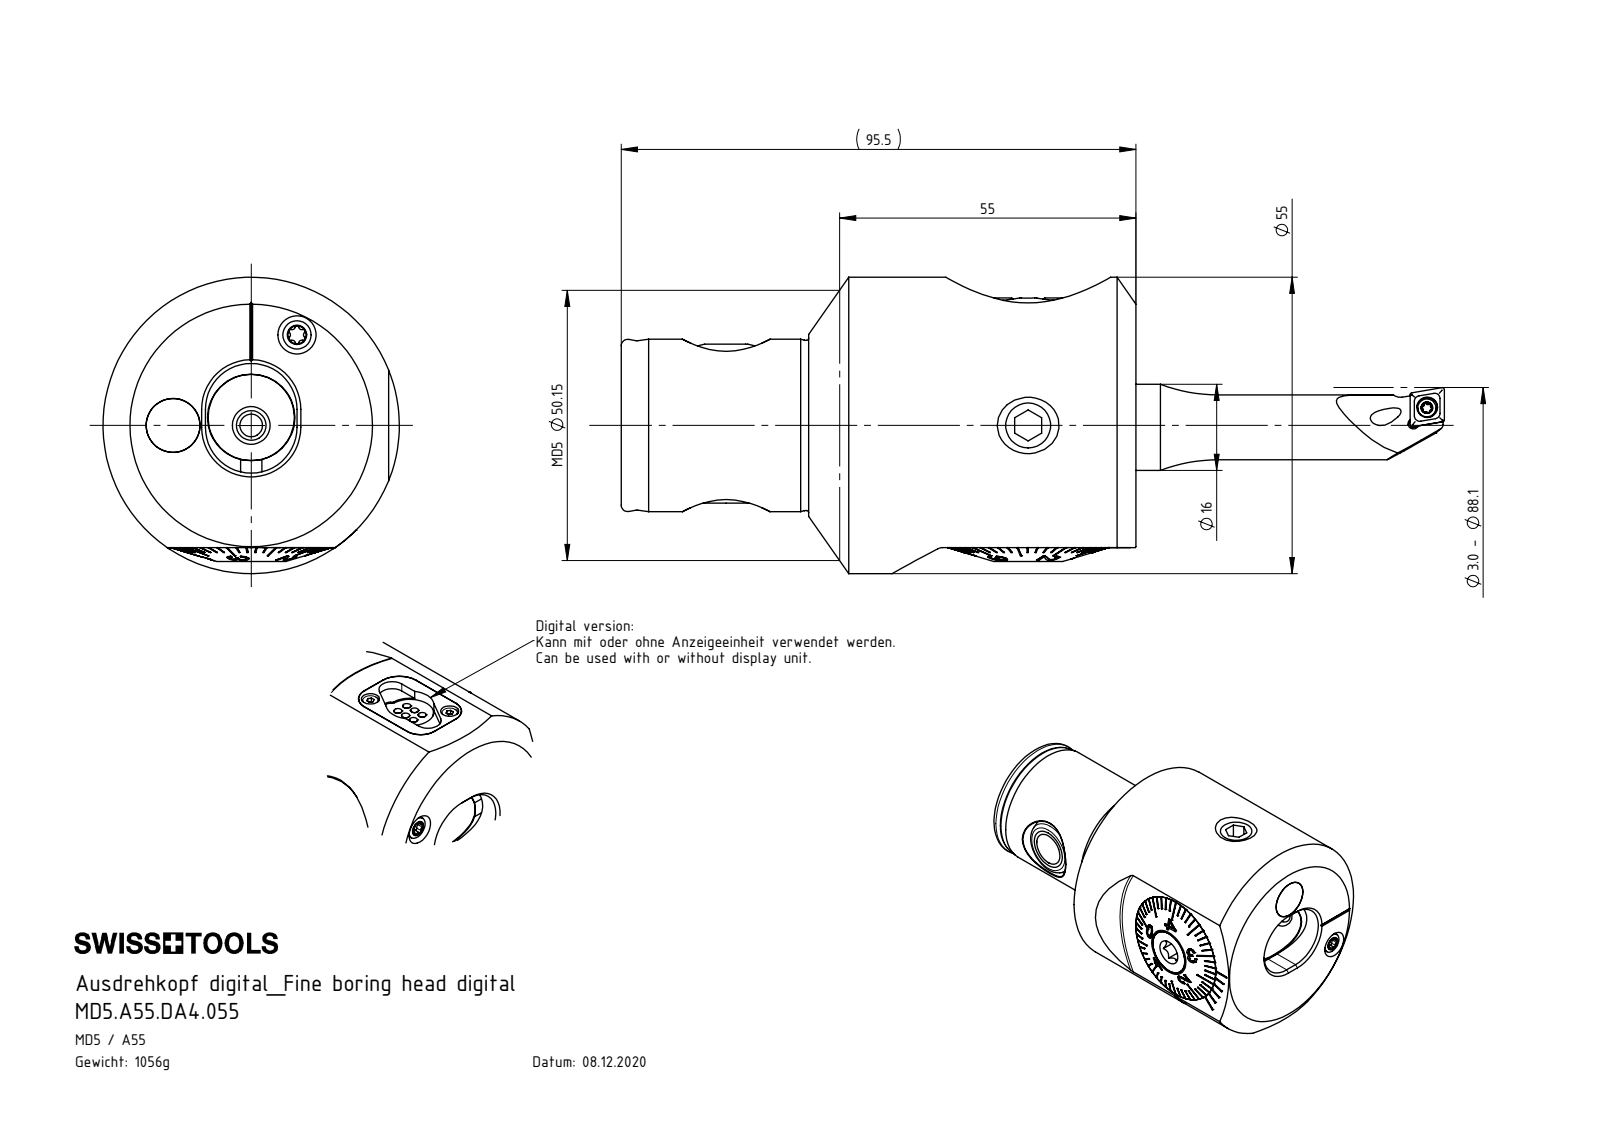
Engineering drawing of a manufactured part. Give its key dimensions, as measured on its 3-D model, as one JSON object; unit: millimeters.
{"part_name": "A55-BG1.DA4.041; DIN 3771 - 17x2; ISO 4026 - M10 x 16_PreviewCfg; Klebstoff D10 (+8 more)", "step_written_by": "SolidWorks 2017 (AUTOMOTIVE_DESIGN)", "units": "millimeters", "bodies": {"solids": 38, "faces": 1147, "planar": 505, "cylindrical": 246, "other": 396}, "overall_size": [95.54, 55, 55], "volume_mm3": 137303, "surface_area_mm2": 48089, "round_holes": [[4.2, 4], [1.6, 3], [8.5, 3], [2.2, 2], [10, 2], [3.3, 1], [6, 1], [7, 1], [8, 1], [8.75, 1], [10.1, 1], [11, 1]], "round_bosses_or_shafts": [[1.9, 6], [10, 4], [3.8, 2], [2, 2], [55, 1], [32, 1], [31.6, 1], [30, 1]], "partial_cylinders_radius": [[0.34, 6], [0.59, 6], [1.1, 6], [1.2, 6], [0.5, 4], [0.8, 4], [1.4, 4], [1.9, 4]], "face_to_face_distances": [95.54, 5.3, 7.13, 4.63, 2.5, 1.83, 2.8, 8.33, 6.5, 3.7], "hole_center_spacings": [7.25, 9.52, 14.5, 1.48, 14.58, 17.52, 18.83, 19.04]}
